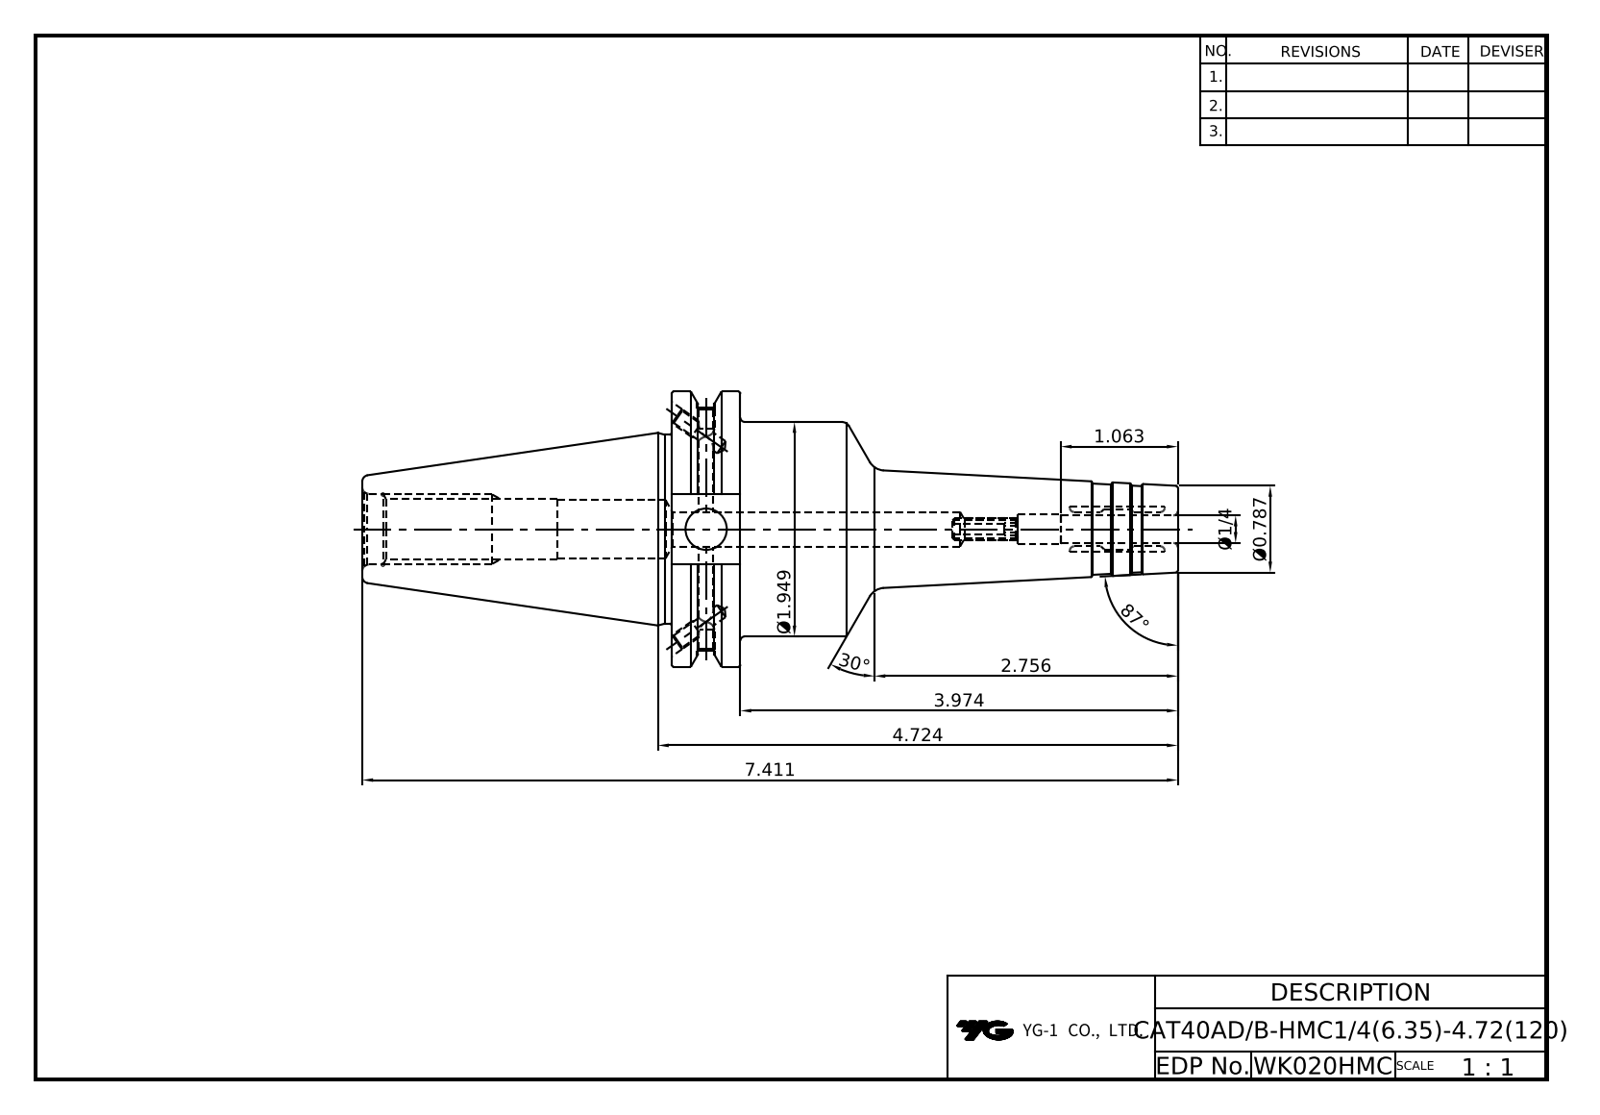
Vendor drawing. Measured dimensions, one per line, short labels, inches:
name: WK020HMC-CAT40ADB-HMC0_25-4_72
written by: PRO/ENGINEER BY PARAMETRIC TECHNOLOGY CORPORATION, 2012130 (CONFIG_CONTROL_DESIGN)
unit: in
bodies: 1 solid, 187 faces (35 planar, 67 cylindrical, 85 other)
size: 7.411 × 2.5 × 2.416
volume: 11.2 in³; area: 51.03 in²
holes: 3× ⌀0.13, 3× ⌀0.138, 3× ⌀0.157, 2× ⌀0.165, 1× ⌀0.169, 1× ⌀0.25, 1× ⌀0.268, 1× ⌀0.315, 1× ⌀0.375, 1× ⌀0.531, 1× ⌀0.551, 1× ⌀0.642
bosses: 1× ⌀2.5, 1× ⌀1.948, 1× ⌀1.717
rounds: 1× R0.322, 1× R1.108
face distances: 0.625, 4.599, 3.974, 1.898, 0.644, 0.239, 0.386, 4.36, 0.389, 0.15
